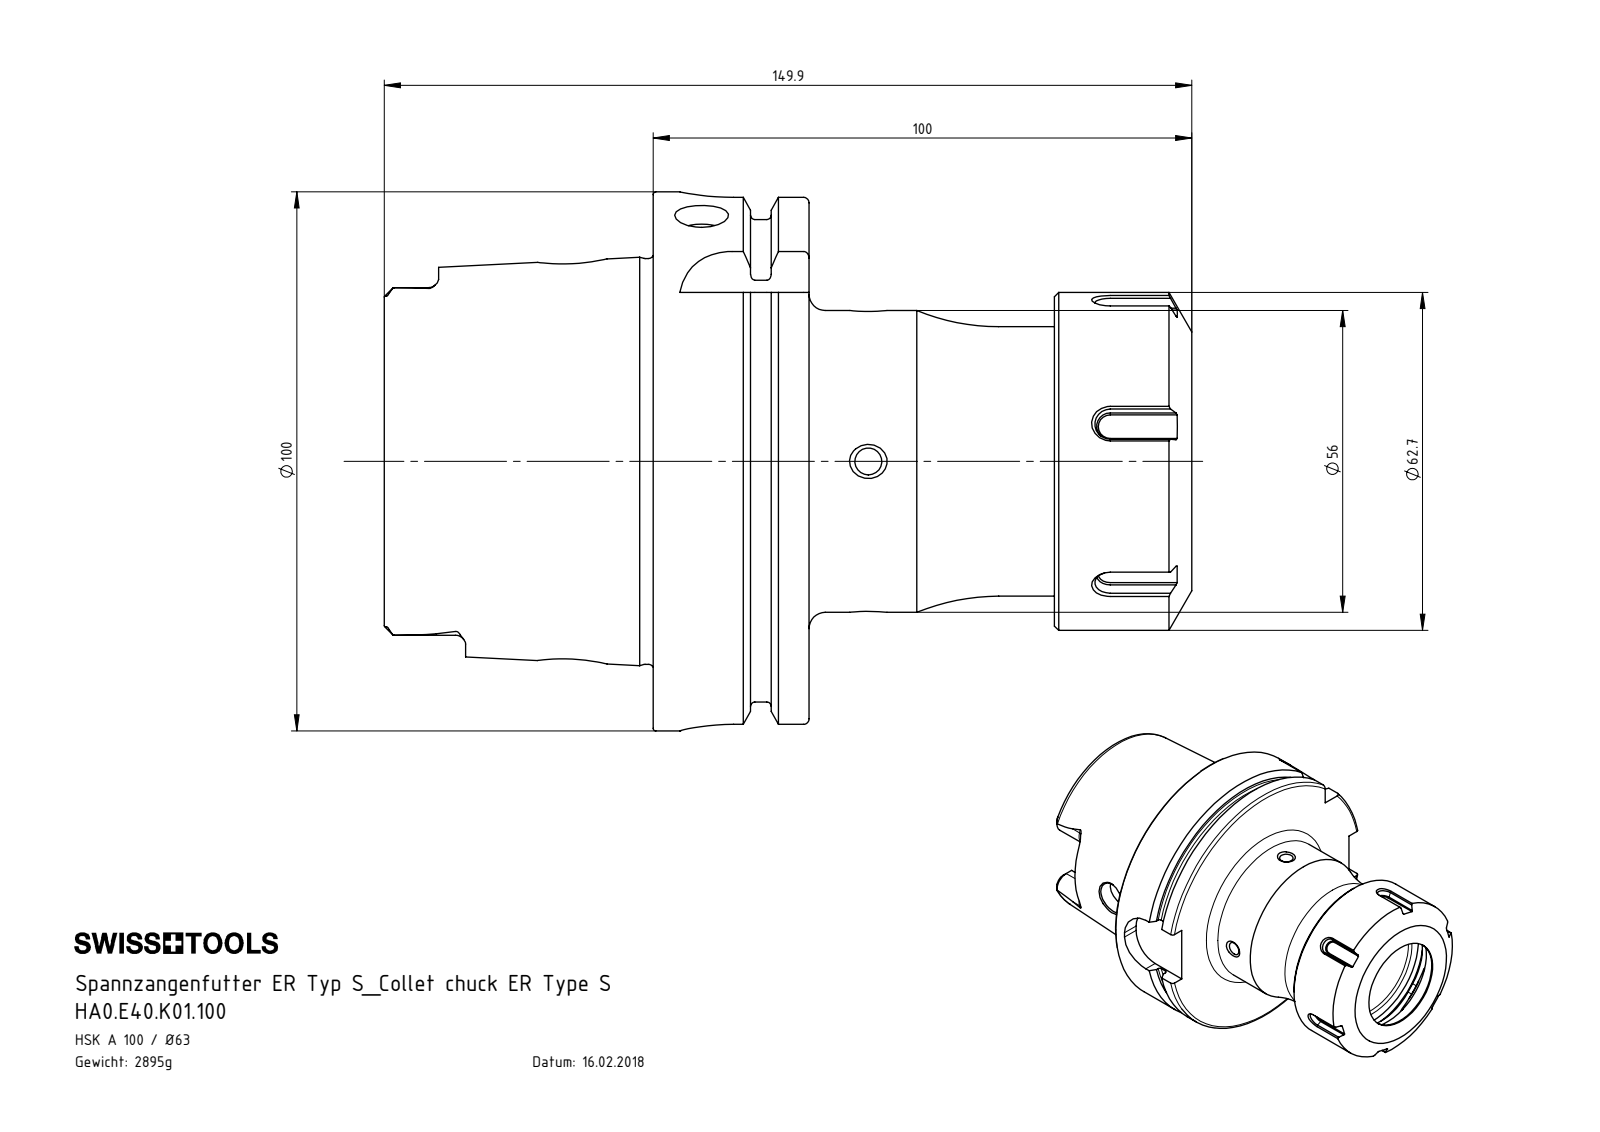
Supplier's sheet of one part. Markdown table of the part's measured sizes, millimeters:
| quantity | value |
| --- | --- |
| part name | HA0-E40.K01.100_C_Fertigbearbeitung; HA0.E40.K01.100; E40-ER1.001.025 |
| STEP written by | SolidWorks 2017 (CONFIG_CONTROL_DESIGN) |
| units | millimeters |
| bodies | 2 solids, 283 faces (93 planar, 73 cylindrical, 117 other) |
| overall size | 149.9 × 100 × 100 |
| volume | 368 738 mm³ |
| surface area | 75 788 mm² |
| round holes (diameter × count) | 10 × 3, 5 × 2, 11 × 1, 12 × 1, 22.5 × 1, 26 × 1, 30.5 × 1, 33.5 × 1, 48.5 × 1, 50.5 × 1, 53 × 1, 63 × 1 |
| round bosses / shafts (diameter × count) | 100 × 1, 91.95 × 1, 75.26 × 1, 62.7 × 1, 56 × 1, 50 × 1 |
| partial cylindrical surfaces (radius × count) | 1.9 × 6, 4.88 × 4, 10 × 4, 19.26 × 2 |
| main face-to-face distances | 28.95, 12.45, 16.5, 74.5, 62.05, 45.55, 100, 87.55, 71.05, 25.5 |
| hole center spacings | 32.95, 54.95 |
